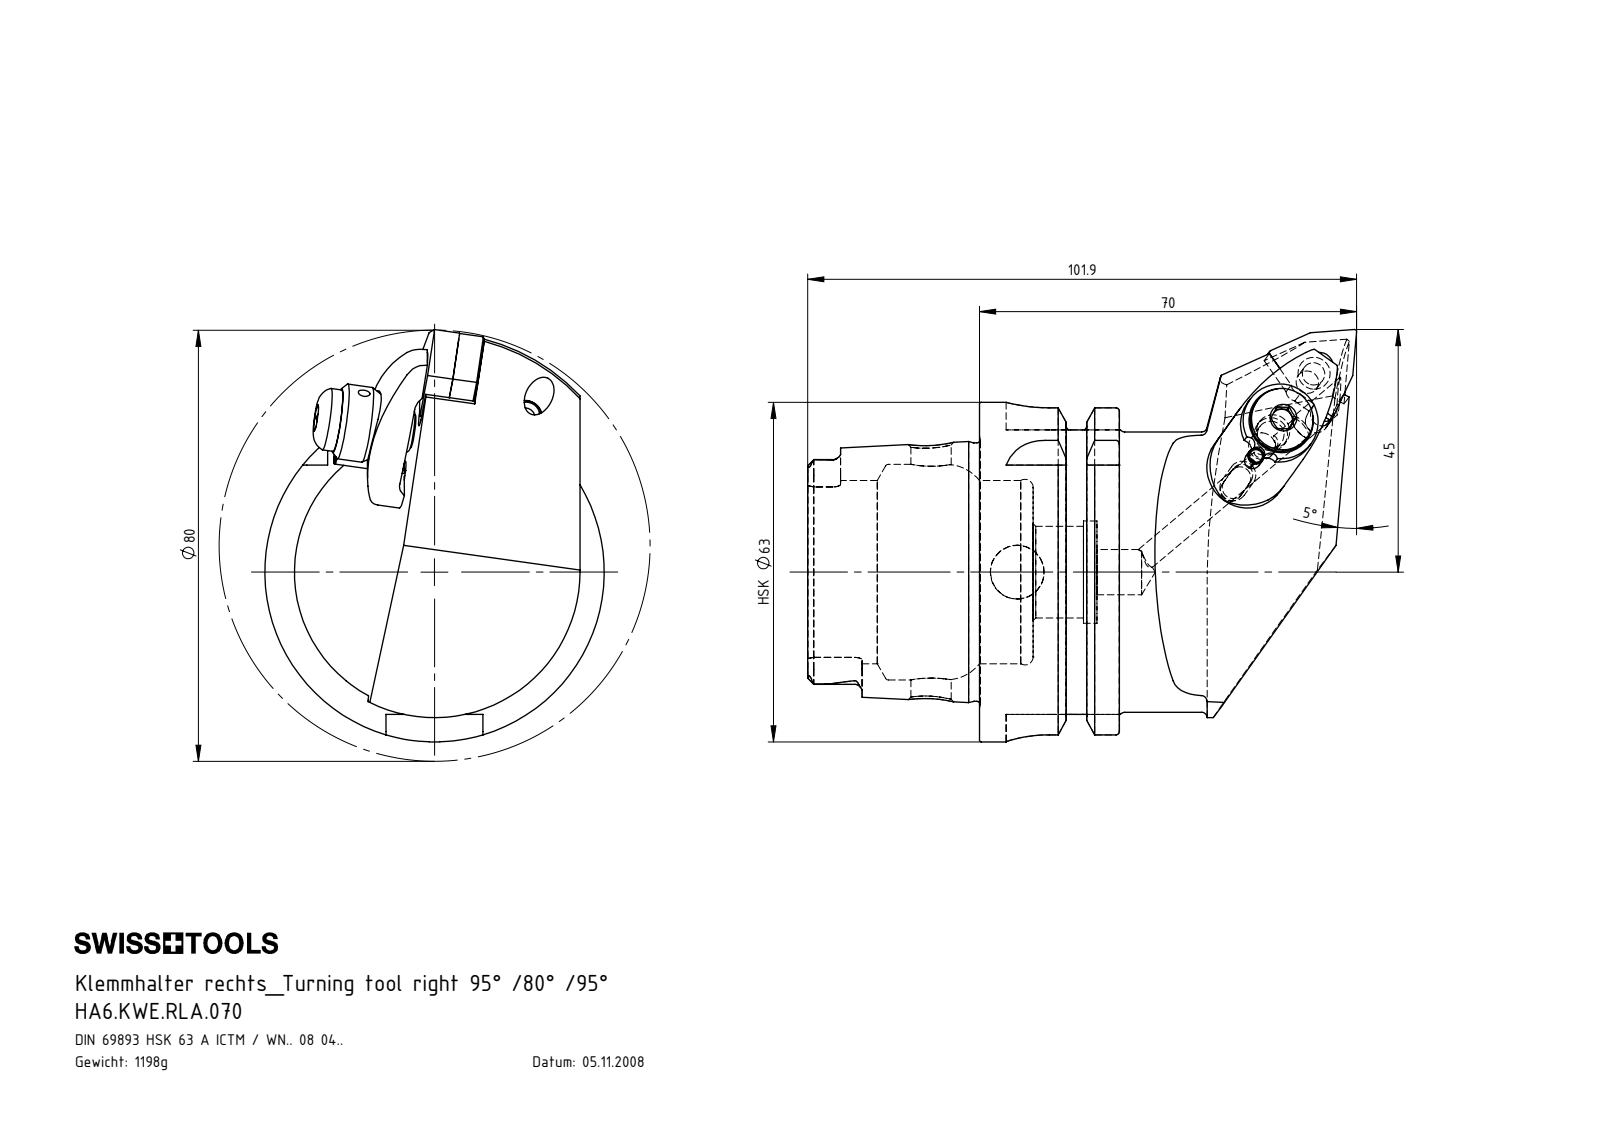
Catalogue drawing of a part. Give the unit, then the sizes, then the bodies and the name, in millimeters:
Units: millimetres
Overall size (bounding box): 101.9 × 76.5 × 63
Round holes (diameter × count): ⌀2 ×3, ⌀4.2 ×2, ⌀5 ×2, ⌀7 ×2, ⌀2.4 ×1, ⌀3 ×1, ⌀4 ×1, ⌀5.16 ×1, ⌀6.2 ×1, ⌀6.7 ×1, ⌀7.5 ×1, ⌀7.8 ×1
Round bosses / shafts (diameter × count): ⌀5 ×2, ⌀3 ×2, ⌀63 ×1, ⌀54.95 ×1, ⌀52 ×1, ⌀47.94 ×1, ⌀14 ×1, ⌀11.5 ×1
Partial cylindrical surfaces — rounded edges, fillets, slot ends (radius × count): R0.39 ×6, R0.69 ×6, R1.4 ×6, R0.4 ×4, R8 ×4, R1.5 ×3, R2 ×3, R2.82 ×2
Main face-to-face distances: 25.95, 16, 9.95, 31.9, 41.85, 57.85, 4.76, 52.8, 21.8, 11.85
Hole centre spacings: 8, 0.31, 14.77, 22.77, 7.99, 8.2, 8.21, 14.53
Volume: 151 981 mm³ · Surface area: 35 449 mm²
Bodies: 11 solids, 483 faces (135 planar, 154 cylindrical, 194 other)
Part name (STEP PRODUCT): WNMG080404; WCC-ER3.102.024_C; HA6.KWE.RLA.070; WCC-ER2.001.010_A (+7 more)
STEP written by: SolidWorks 2017 (AUTOMOTIVE_DESIGN)
